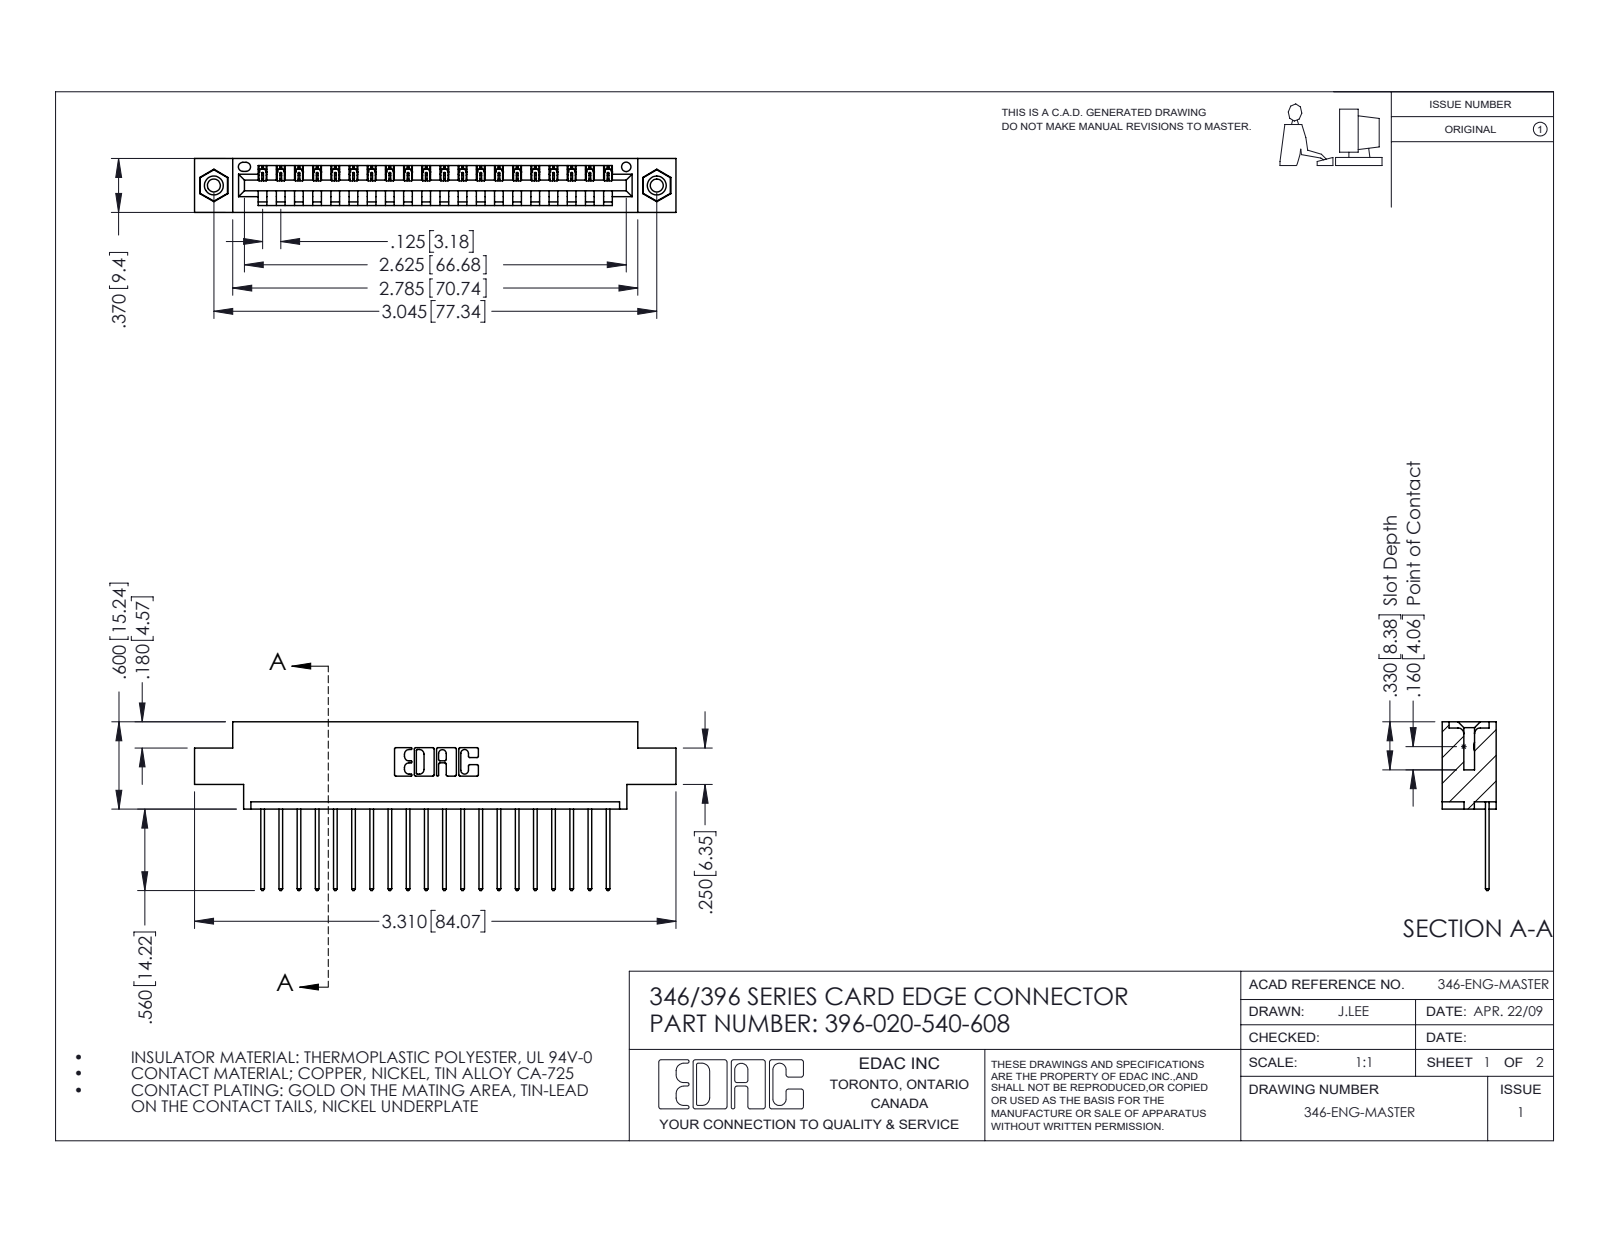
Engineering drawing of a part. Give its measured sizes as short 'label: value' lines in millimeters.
name: 345-250-001_345-250-003-102; 396-020-540-608; 346 Part_0.170 Offset - 0.156 Dia-TI; 345-292-001_345-293-140
written by: SolidWorks 2016 (CONFIG_CONTROL_DESIGN)
unit: mm
bodies: 23 solids, 1346 faces (912 planar, 418 cylindrical, 16 other)
size: 84.1 × 29.5 × 9.4
volume: 7 770 mm³; area: 9 845 mm²
holes: 2× ⌀2.3, 2× ⌀3.2, 2× ⌀4, 1× ⌀1.6
bosses: 2× ⌀3.9
rounds: 40× R0.2, 40× R0.3, 22× R0.3, 6× R0.2, 6× R0.8, 3× R0.7, 2× R0.8, 2× R1
face distances: 1.2, 8.2, 9.4, 6.4, 1.8, 7.6, 0.6, 5.6, 3.8, 2.5
hole spacings: 6.2, 72.1, 77.3
